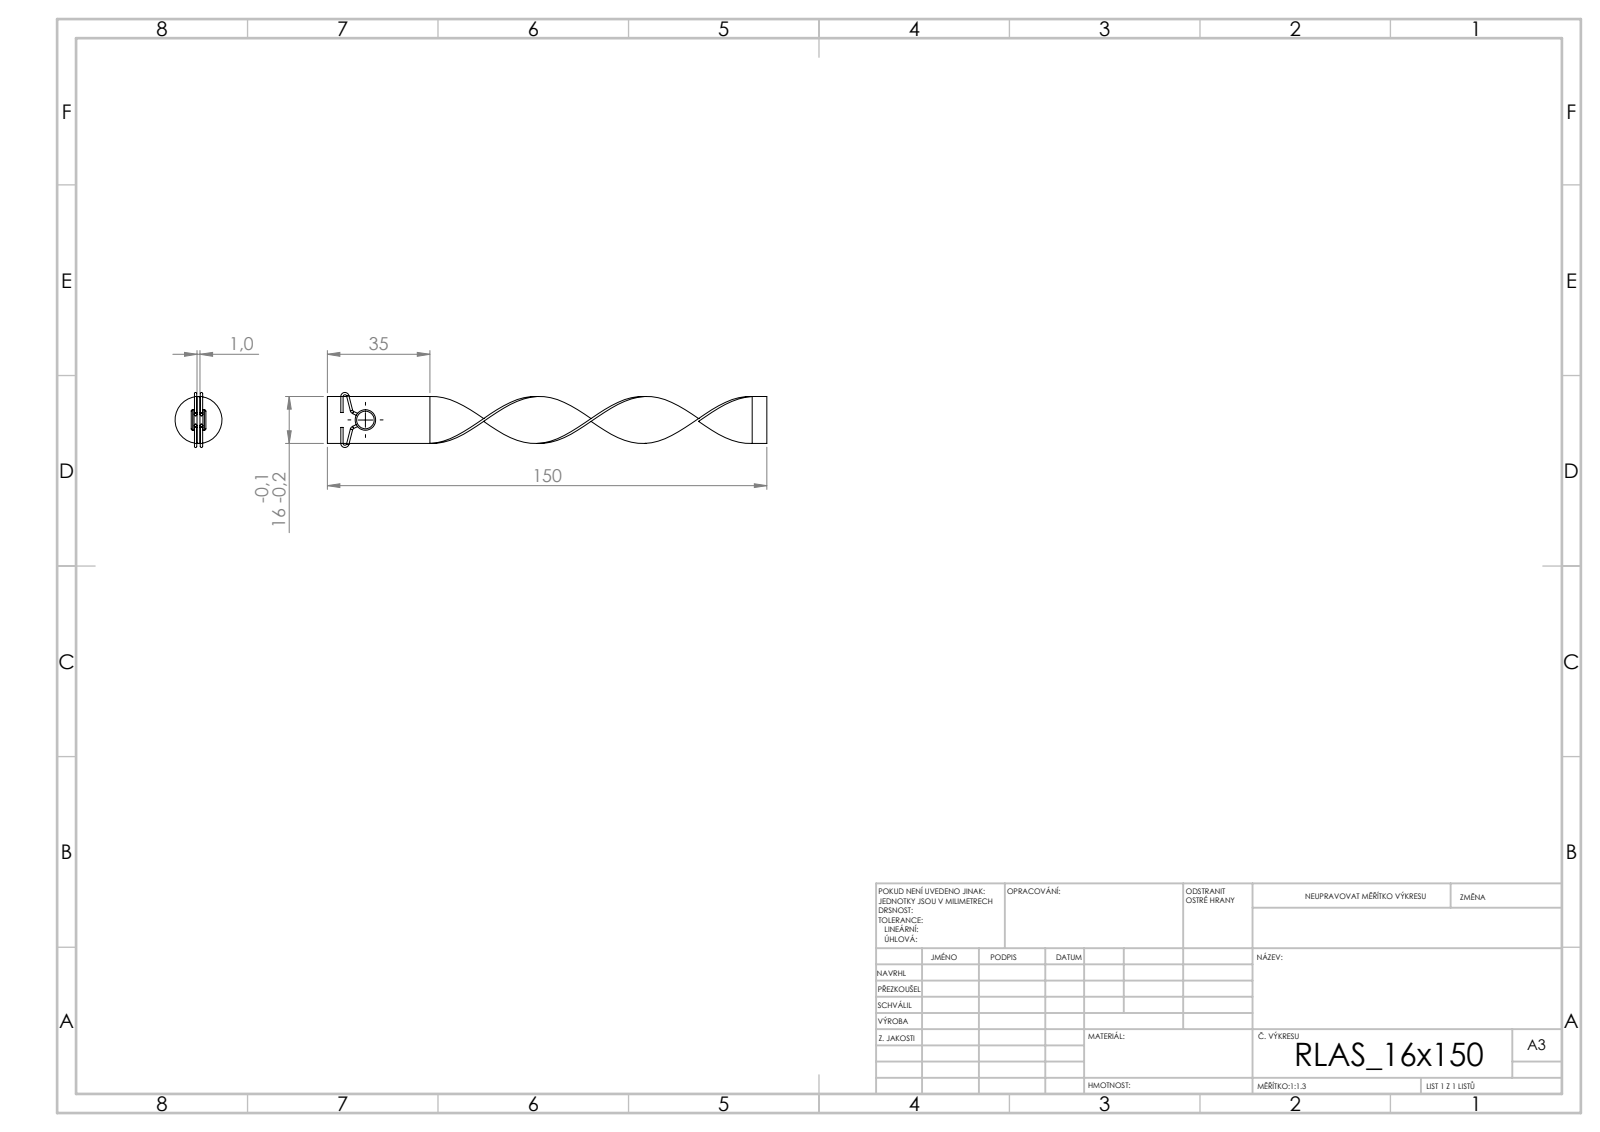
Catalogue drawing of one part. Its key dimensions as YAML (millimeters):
step_written_by: "SolidWorks 2019 (CONFIG_CONTROL_DESIGN)"
units: millimeters
bodies: {solids: 3, faces: 90, planar: 18, cylindrical: 40, other: 32}
overall_size: [150, 18.8, 16.03]
volume: 2547
surface_area: 5788
round_bosses_or_shafts:
  - {diameter: 0.8, count: 14}
  - {diameter: 7, count: 1}
  - {diameter: 4, count: 1}
face_to_face_distances: [1, 2, 3, 4, 16, 5, 150, 5.45, 10.55, 5.1]
